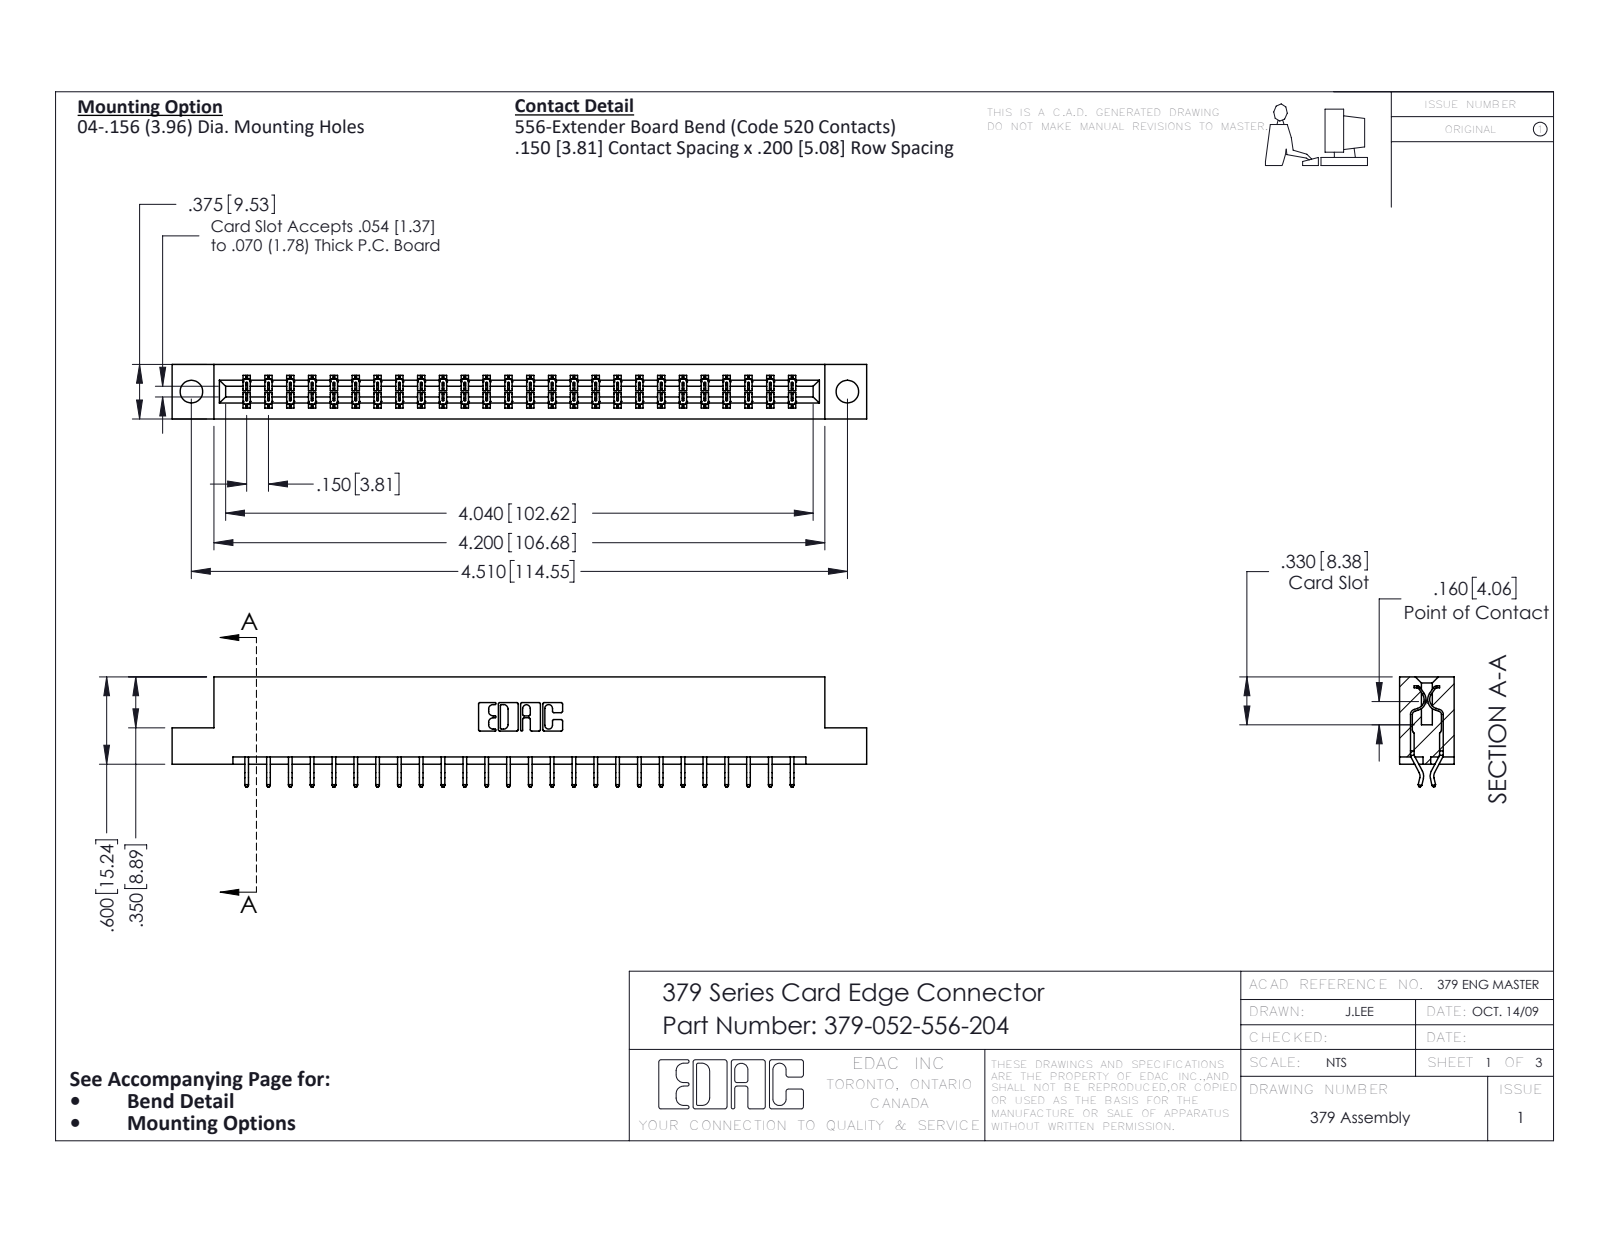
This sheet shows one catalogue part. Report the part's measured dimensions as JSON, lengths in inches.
{"part_name": "345-292-001_556 Tail; 379 Part_Flush - .156 Dia - TH; 379-052-556-204", "step_written_by": "SolidWorks 2016 (CONFIG_CONTROL_DESIGN)", "units": "inches", "bodies": {"solids": 53, "faces": 3130, "planar": 2150, "cylindrical": 980, "other": 0}, "overall_size": [4.775, 0.757, 0.375], "volume_in3": 0.771, "surface_area_in2": 21.36, "round_holes": [[0.156, 2]], "partial_cylinders_radius": [[0.006, 78], [0.01, 22], [0.007, 6], [0.031, 6], [0.026, 3], [0.01, 2], [0.014, 2], [0.022, 2]], "face_to_face_distances": [0.3, 0.075, 0.375, 0.2, 0.225, 0.1, 0.55, 0.076, 0.15, 0.05], "hole_center_spacings": [4.51]}
